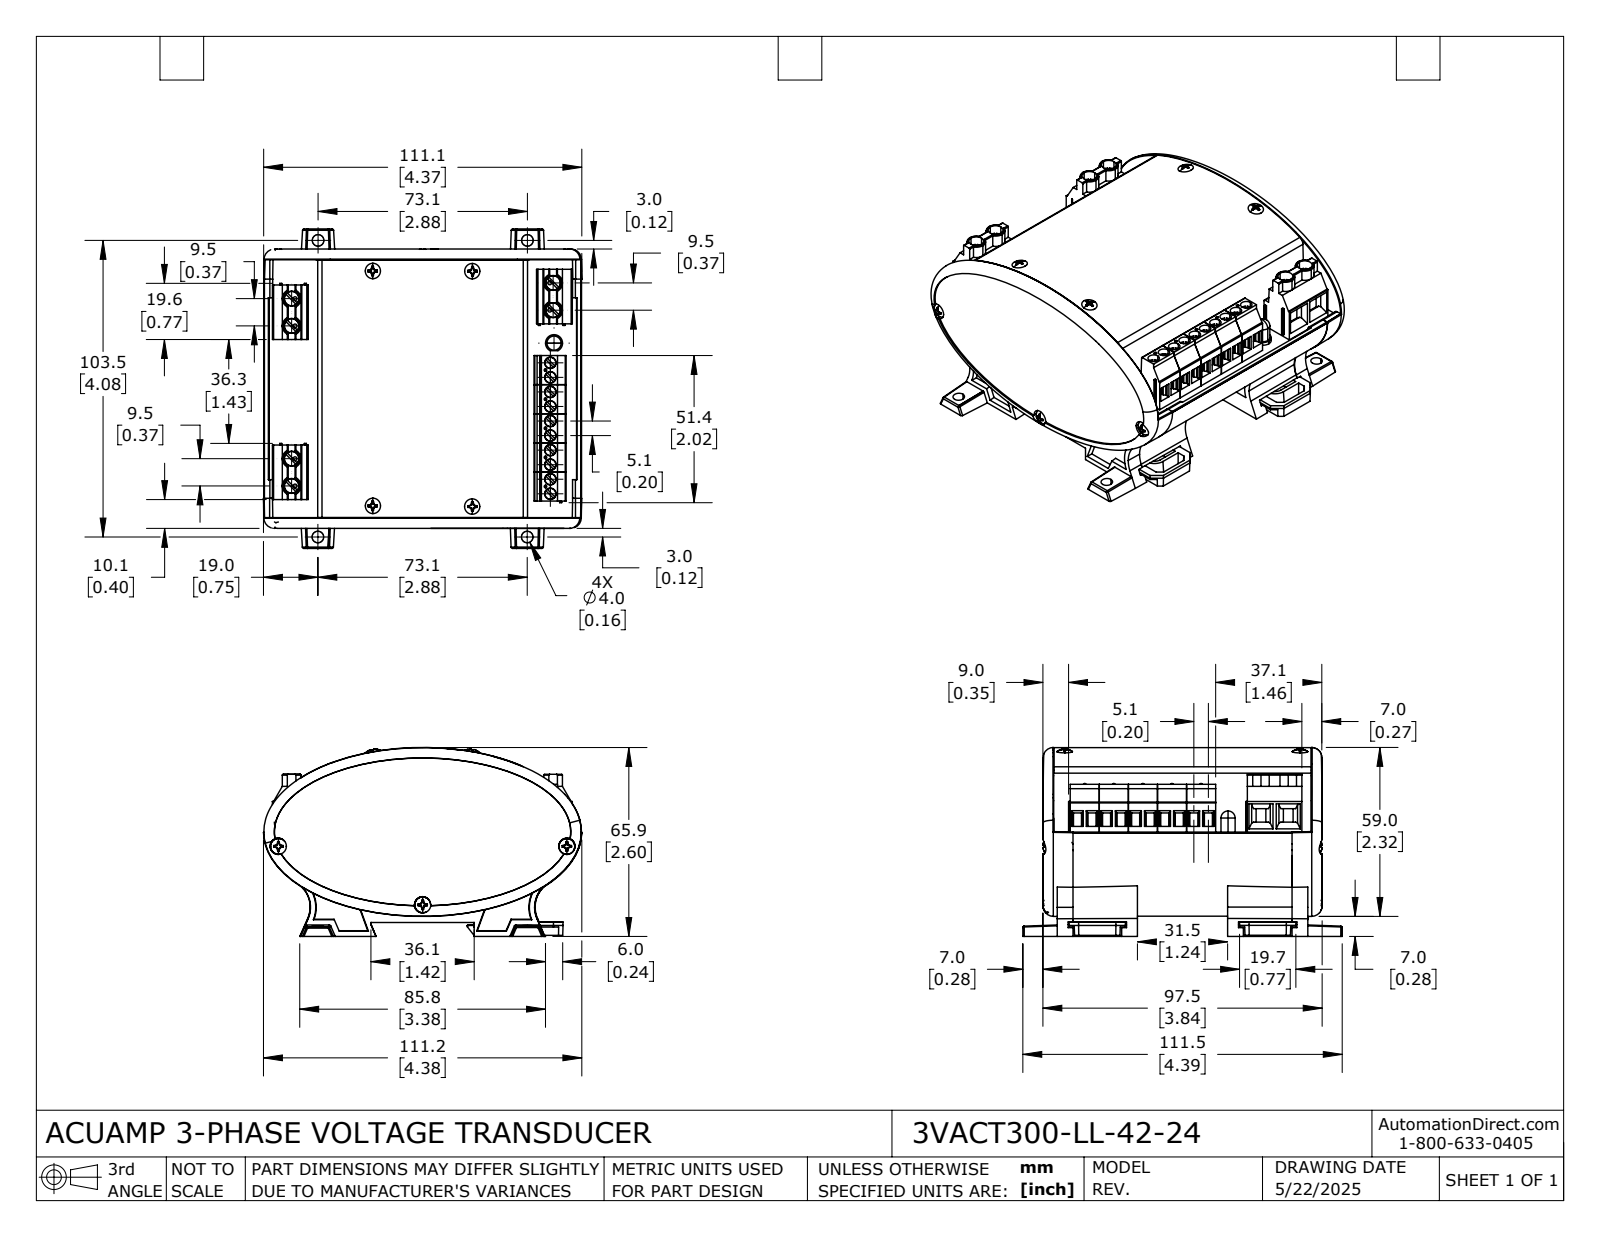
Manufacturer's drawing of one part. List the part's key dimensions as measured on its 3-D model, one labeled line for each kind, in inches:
Part name (STEP PRODUCT): 3VACT300-LL-42-24
STEP written by: SolidWorks 2024 (AUTOMOTIVE_DESIGN)
Units: inches
Bodies: 26 solids, 2965 faces (1484 planar, 838 cylindrical, 643 other)
Overall size (bounding box): 4.391 × 4.377 × 2.597
Volume: 8.539 in³ · Surface area: 197.4 in²
Round holes (diameter × count): ⌀0.05 ×12, ⌀0.157 ×10, ⌀0.08 ×6, ⌀0.111 ×6, ⌀0.205 ×6, ⌀0.126 ×4
Round bosses / shafts (diameter × count): ⌀0.051 ×16, ⌀0.15 ×10, ⌀0.112 ×10, ⌀0.067 ×10, ⌀0.197 ×6, ⌀0.018 ×4, ⌀0.234 ×1, ⌀0.194 ×1
Partial cylindrical surfaces — rounded edges, fillets, slot ends (radius × count): R0.006 ×40, R0.039 ×20, R0.008 ×16, R0.02 ×16, R0.01 ×6, R0.012 ×6, R0.128 ×6, R0.018 ×4
Main face-to-face distances: 0.063, 0.128, 3.672, 3.8, 3.543, 0.084, 0.394, 3.406, 0.266, 3.278
Hole centre spacings: 0.2, 0.4, 0.6, 0.8, 1, 1.2, 1.4, 1.6
